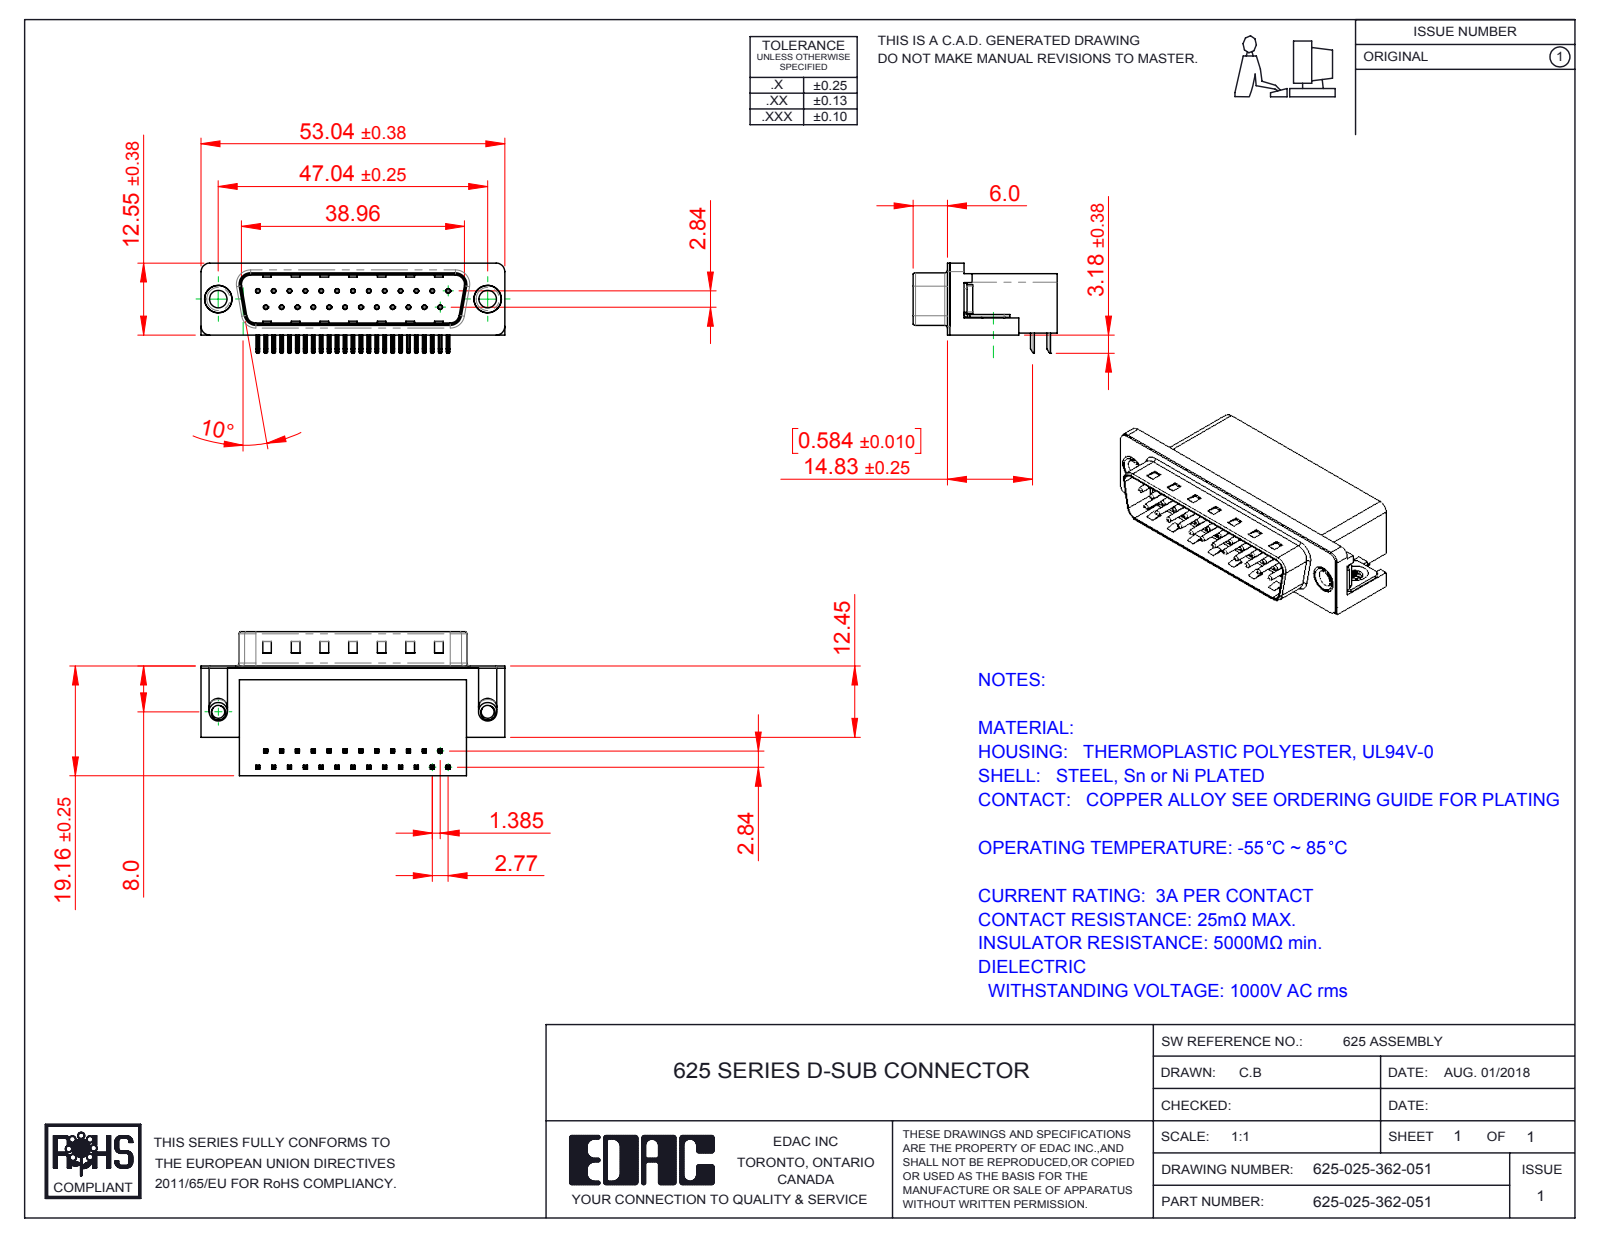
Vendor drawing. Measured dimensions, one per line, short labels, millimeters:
name: 625 Housing_25 Socket; 625 Shell_25 Socket; 625-025-362-051; 625 Thru Hole Rivet (+3 more)
written by: SolidWorks 2016 (CONFIG_CONTROL_DESIGN)
unit: mm
bodies: 31 solids, 2257 faces (1407 planar, 655 cylindrical, 195 other)
size: 53.04 × 25.16 × 15.73
volume: 9 163 mm³; area: 8 918 mm²
holes: 25× ⌀0.35, 25× ⌀0.8, 2× ⌀2.26, 2× ⌀3.05, 2× ⌀4, 2× ⌀4.8, 2× ⌀5
bosses: 25× ⌀0.75, 2× ⌀4.9, 2× ⌀4.75, 2× ⌀3.85, 2× ⌀3.26
rounds: 108× R0.25, 50× R0.12, 16× R1, 9× R0.5, 8× R1.6, 7× R1.5, 4× R0.9, 4× R2
face distances: 0.4, 10.35, 18.76, 2.1, 8.76, 10.46, 10.86, 1.7, 19.16, 10.11
hole spacings: 3.16, 2.77, 11.08, 5.54, 8.31, 5.03, 13.85, 7.48
